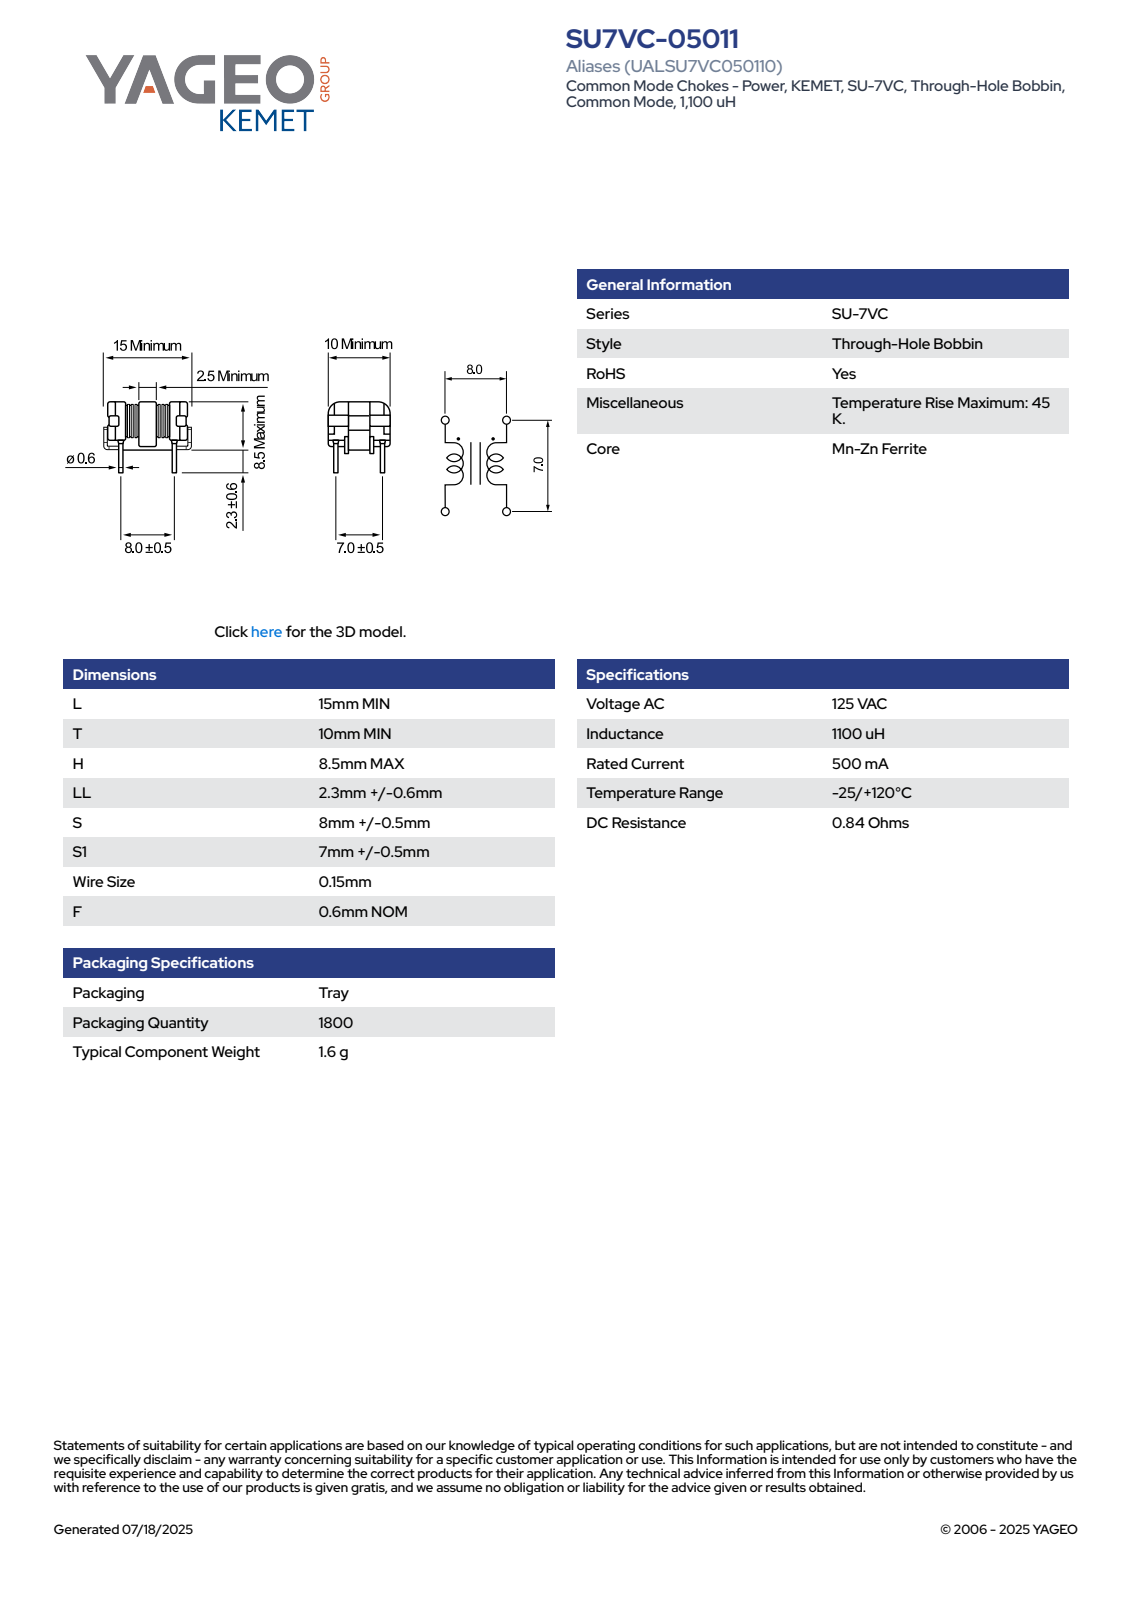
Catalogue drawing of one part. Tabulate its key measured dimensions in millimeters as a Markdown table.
| quantity | value |
| --- | --- |
| part name | SU7VC(MAX-LOGO) |
| STEP written by | SolidWorks 2018 (AUTOMOTIVE_DESIGN) |
| units | millimeters |
| bodies | 1 solid, 489 faces (237 planar, 172 cylindrical, 80 other) |
| overall size | 15 × 10.7 × 10 |
| volume | 658 mm³ |
| surface area | 1 281 mm² |
| round bosses / shafts (diameter × count) | 0.6 × 4 |
| partial cylindrical surfaces (radius × count) | 0.5 × 30, 0.33 × 24, 0.2 × 20, 0.3 × 12, 0.25 × 4, 0.6 × 4, 0.7 × 2, 1.7 × 2 |
| main face-to-face distances | 2.95, 3.45, 3.6, 0.5, 2.8, 0.65, 0.6, 1.97, 4.57, 2.85 |
